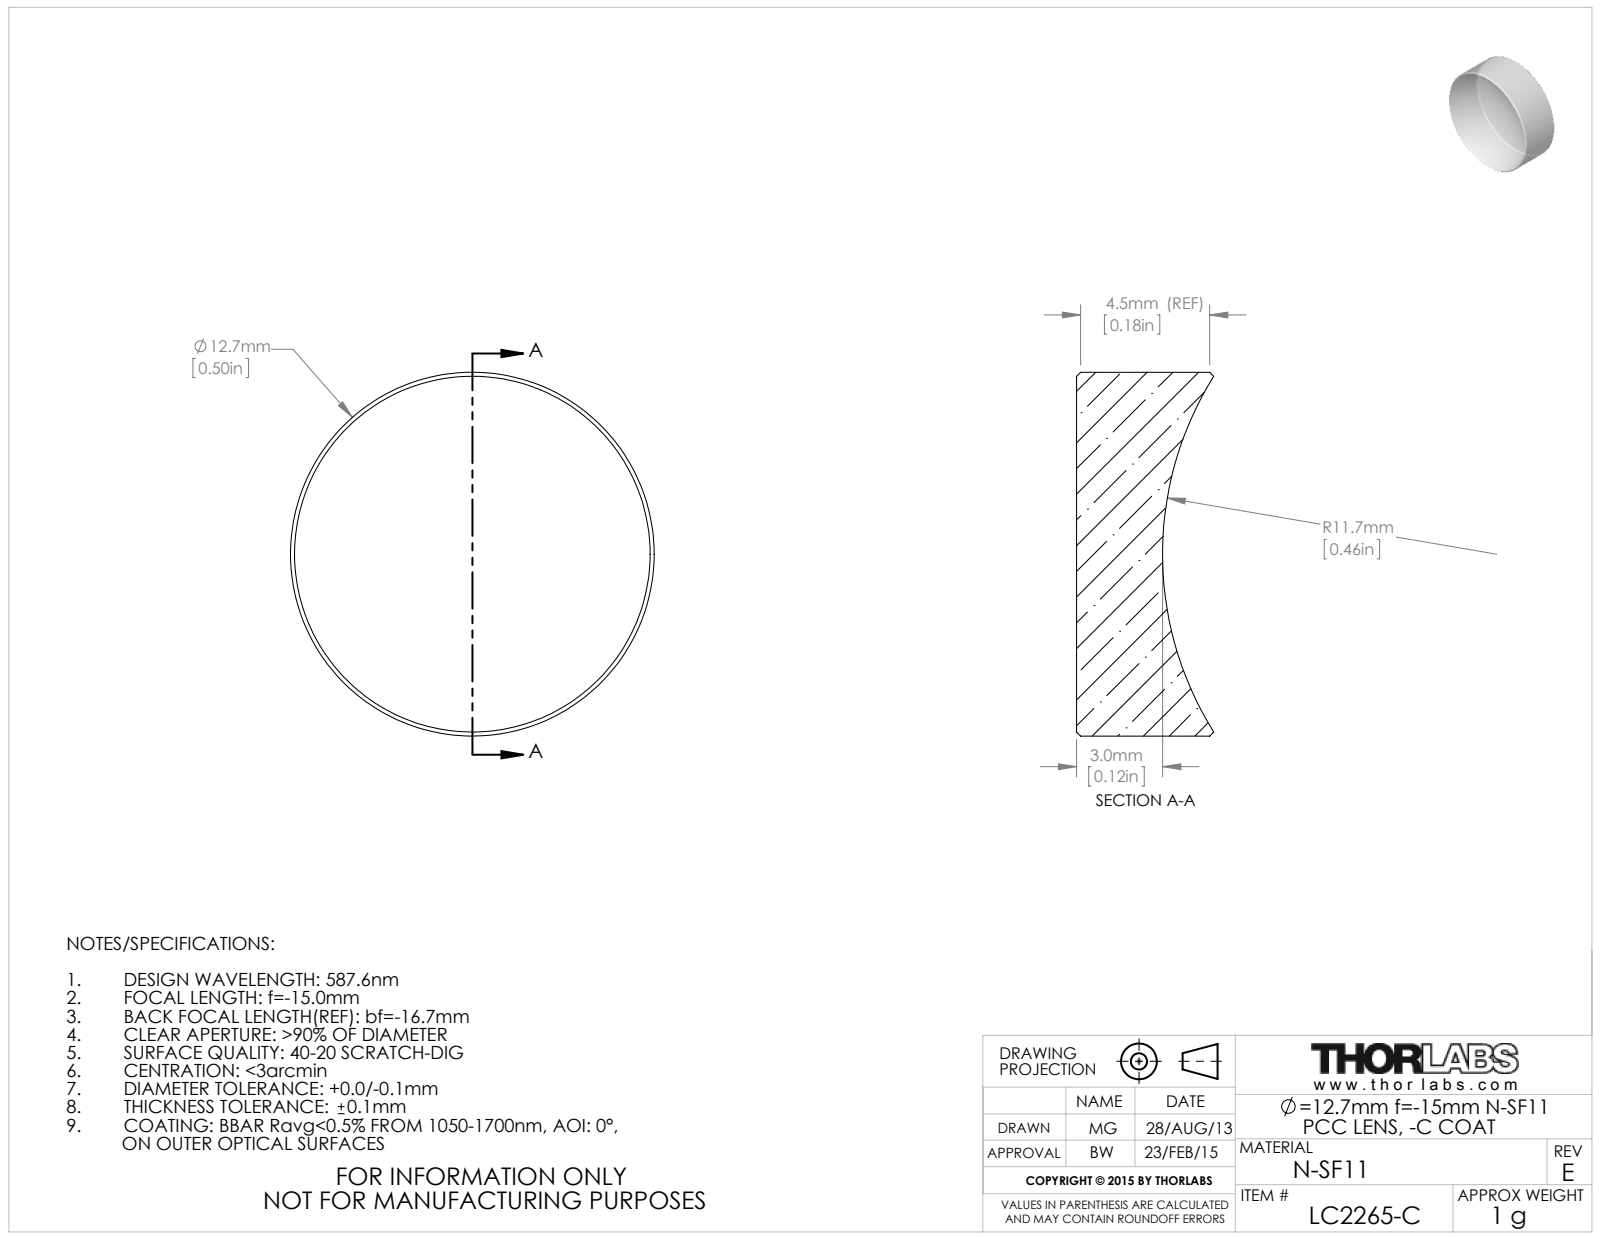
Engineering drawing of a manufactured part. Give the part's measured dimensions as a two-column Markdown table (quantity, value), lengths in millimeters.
| quantity | value |
| --- | --- |
| part name | 5438-E0W |
| STEP written by | SolidWorks 2014 (CONFIG_CONTROL_DESIGN) |
| units | millimeters |
| bodies | 1 solid, 9 faces (1 planar, 2 cylindrical, 6 other) |
| overall size | 12.7 × 12.7 × 4.79 |
| volume | 495 mm³ |
| surface area | 448 mm² |
| round bosses / shafts (diameter × count) | 12.7 × 1 |
